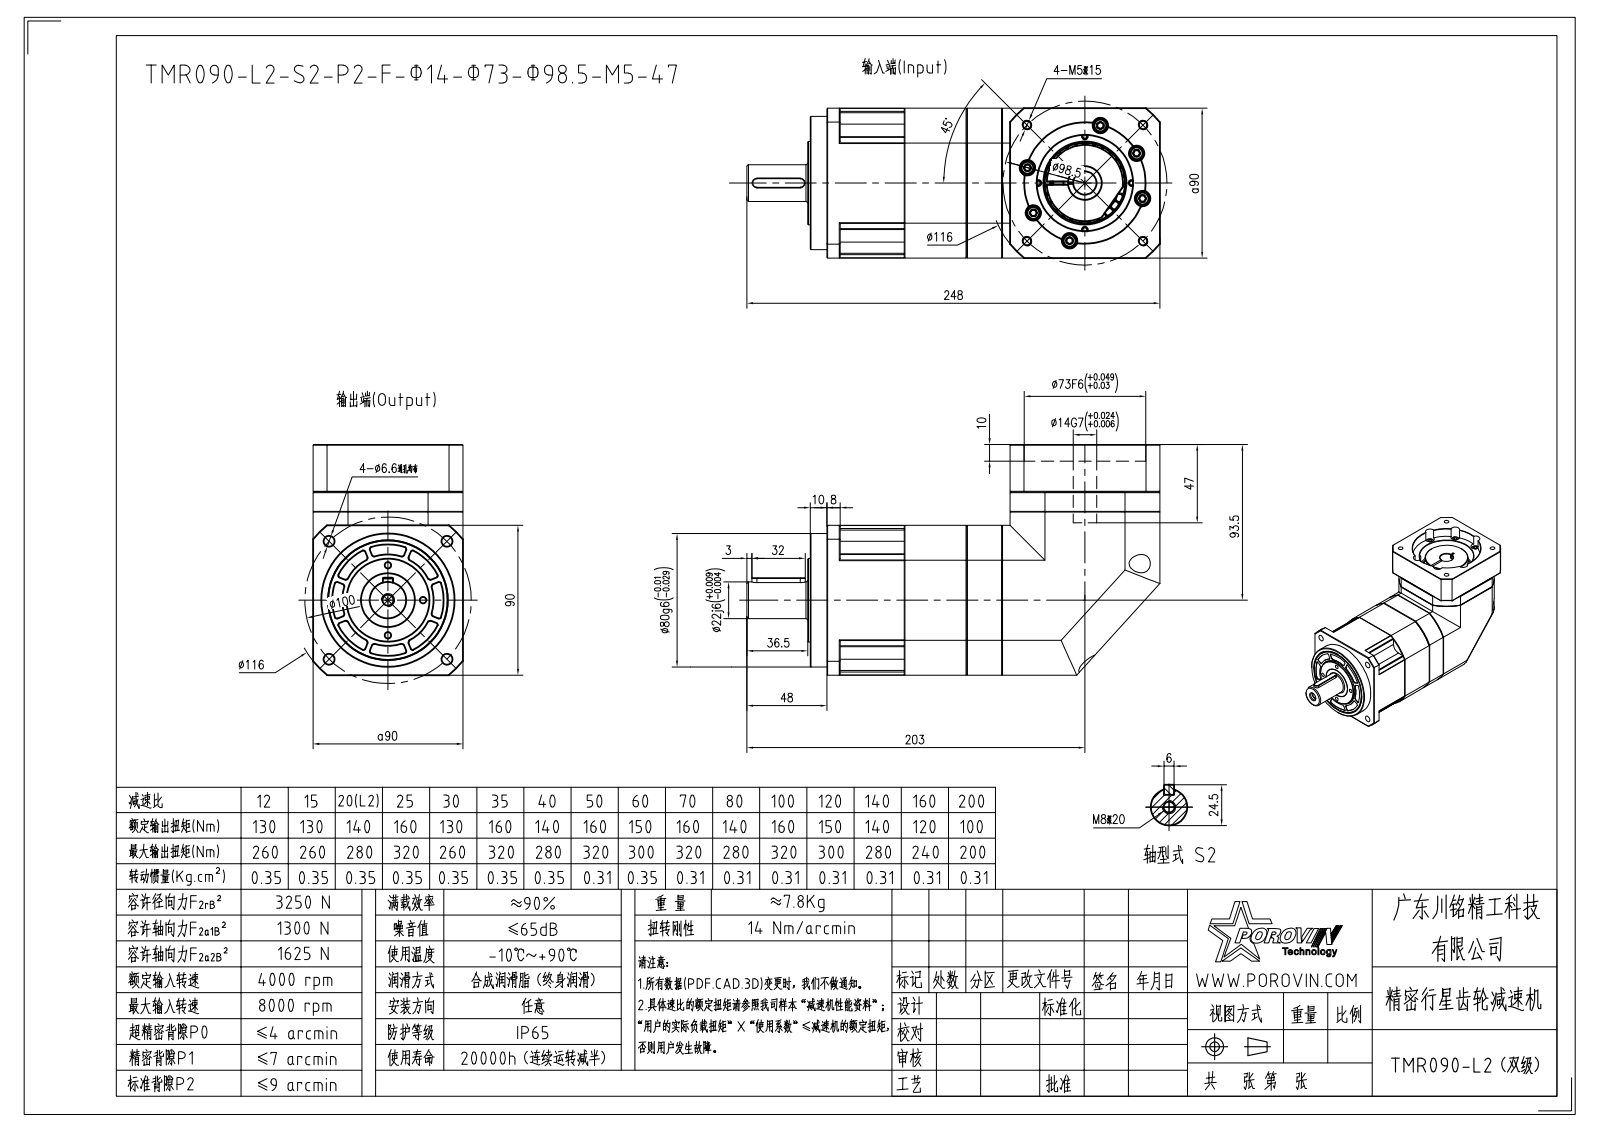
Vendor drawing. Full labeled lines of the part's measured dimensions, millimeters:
Part name (STEP PRODUCT): M900001; HEXAGON_SOCKET_HEAD_CAP_SC-9564; SPRING_LOCK_WASHERS--NORM-19349; HEXAGON_SOCKET_HEAD_CAP_S-19443 (+8 more)
STEP written by: CREO PARAMETRIC BY PTC INC, 2020053 (CONFIG_CONTROL_DESIGN)
Units: millimetres
Bodies: 44 solids, 1333 faces (530 planar, 564 cylindrical, 239 other)
Overall size (bounding box): 248 × 138.5 × 90
Volume: 1 610 000 mm³ · Surface area: 240 270 mm²
Round holes (diameter × count): ⌀5.4 ×12, ⌀5.5 ×12, ⌀9.5 ×12, ⌀4.2 ×11, ⌀6.6 ×10, ⌀6.5 ×5, ⌀4 ×4, ⌀6.68 ×4, ⌀11 ×4, ⌀5 ×1, ⌀6.8 ×1, ⌀8.4 ×1
Round bosses / shafts (diameter × count): ⌀8.5 ×12, ⌀8 ×12, ⌀5 ×12, ⌀10 ×4, ⌀9.88 ×4, ⌀6 ×4, ⌀80 ×1, ⌀78 ×1
Partial cylindrical surfaces — rounded edges, fillets, slot ends (radius × count): R1 ×92, R7.5 ×4, R51 ×3, R3 ×2, R58 ×2, R4 ×1, R5.25 ×1, R20.75 ×1
Main face-to-face distances: 90, 12, 21.5, 21.3, 37.5, 58.8, 59, 110, 10, 98
Hole centre spacings: 35.75, 27.36, 38.16, 44, 66.06, 66.53, 67.94, 13.64
